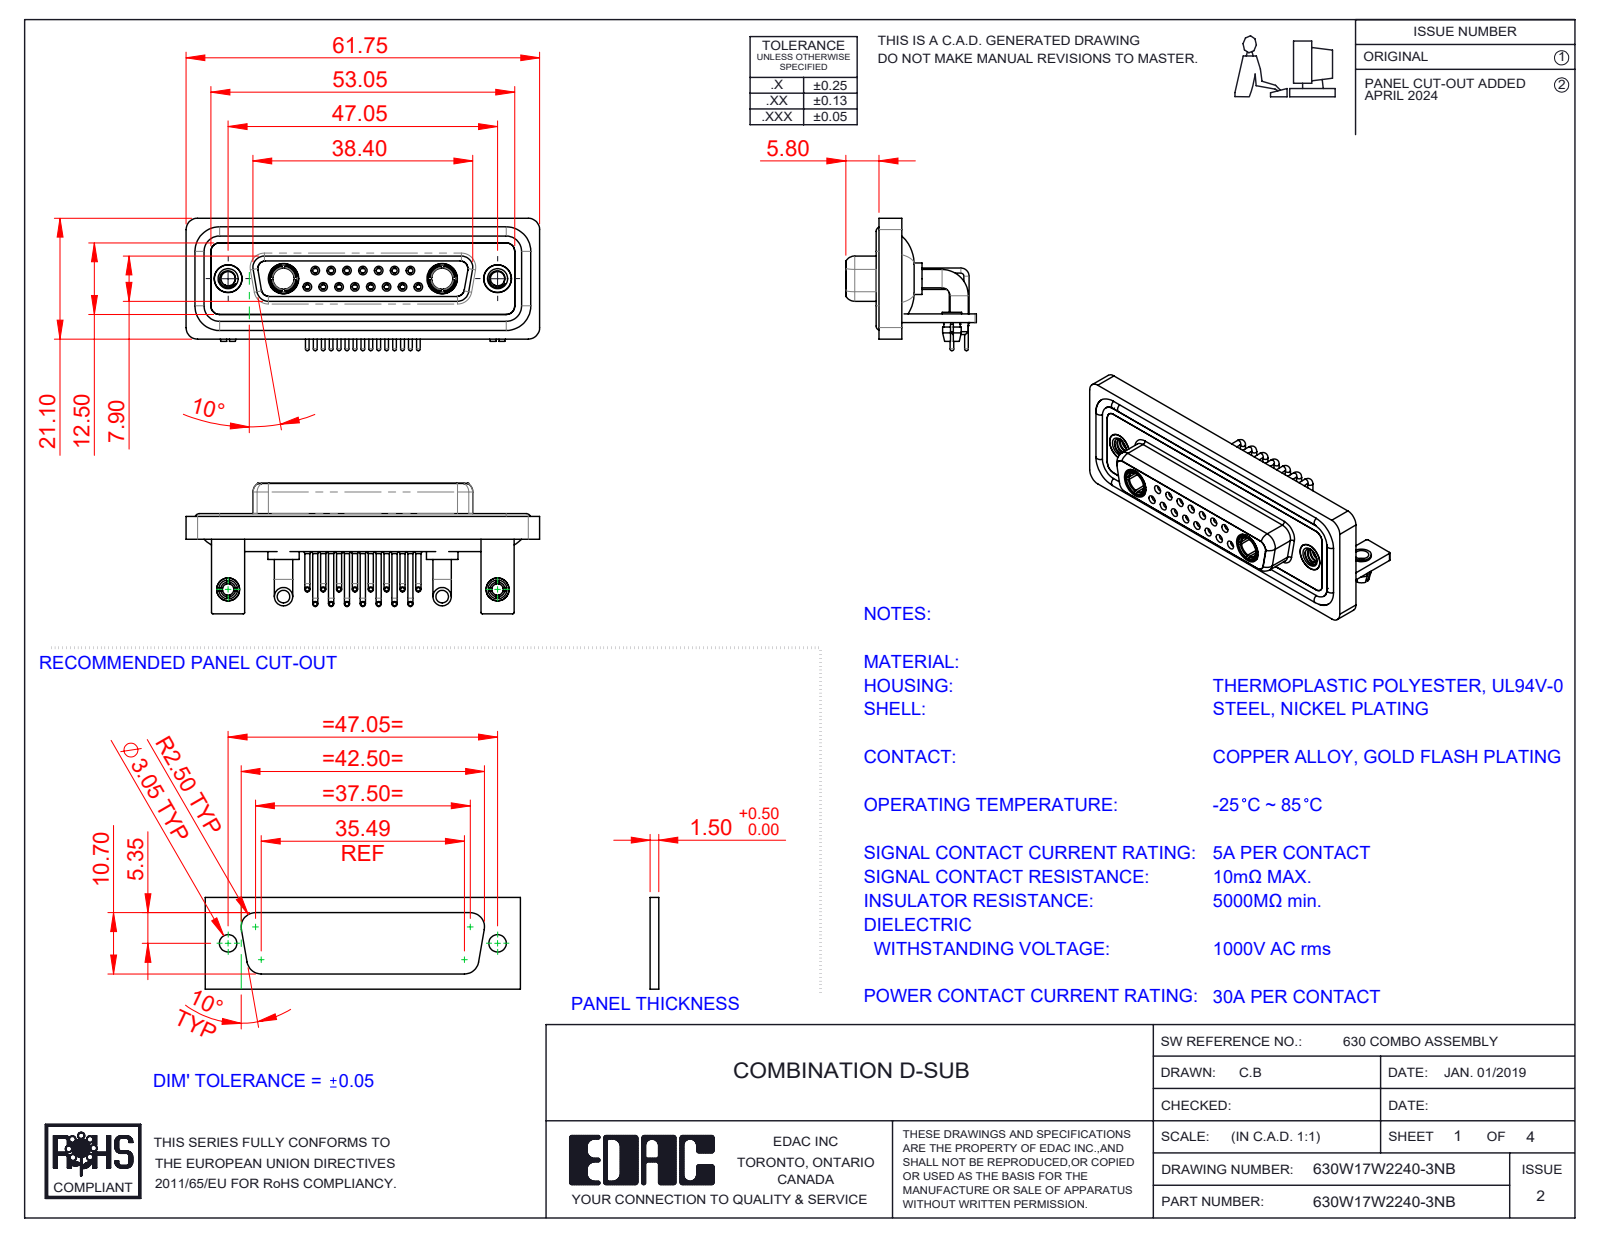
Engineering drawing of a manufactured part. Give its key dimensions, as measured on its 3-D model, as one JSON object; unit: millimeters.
{"part_name": "630W17W2140-3NB; Power Socket_30A RA; 630Combo Threaded Rivet_A; 630Combo Stabilizer Bracket_50 Contacts (+7 more)", "step_written_by": "SolidWorks 2023 (CONFIG_CONTROL_DESIGN)", "units": "millimeters", "bodies": {"solids": 30, "faces": 1471, "planar": 456, "cylindrical": 637, "other": 378}, "overall_size": [61.75, 23.12, 22.8], "volume_mm3": 8938, "surface_area_mm2": 15516, "round_holes": [[2, 17], [0.9, 15], [1.1, 15], [1.5, 15], [1.6, 8], [1.7, 7], [2.5, 4], [4.85, 4], [3.2, 2], [3.7, 2], [4, 2], [4.05, 2]], "round_bosses_or_shafts": [[0.9, 15], [0.65, 15], [1.6, 11], [3.2, 4], [5.5, 2], [5.2, 2], [4.96, 2], [4.95, 2]], "partial_cylinders_radius": [[2, 19], [1.5, 18], [0.25, 16], [1.35, 8], [1.6, 8], [0.5, 5], [0.6, 4], [0.65, 4]], "face_to_face_distances": [0.4, 1.8, 2.9, 3.7, 1.5, 4.1, 1.1, 1.4, 1.6, 3.1], "hole_center_spacings": [3.16, 2.77, 5.54, 8.31, 5.04, 7.49, 11.08, 5.03]}
